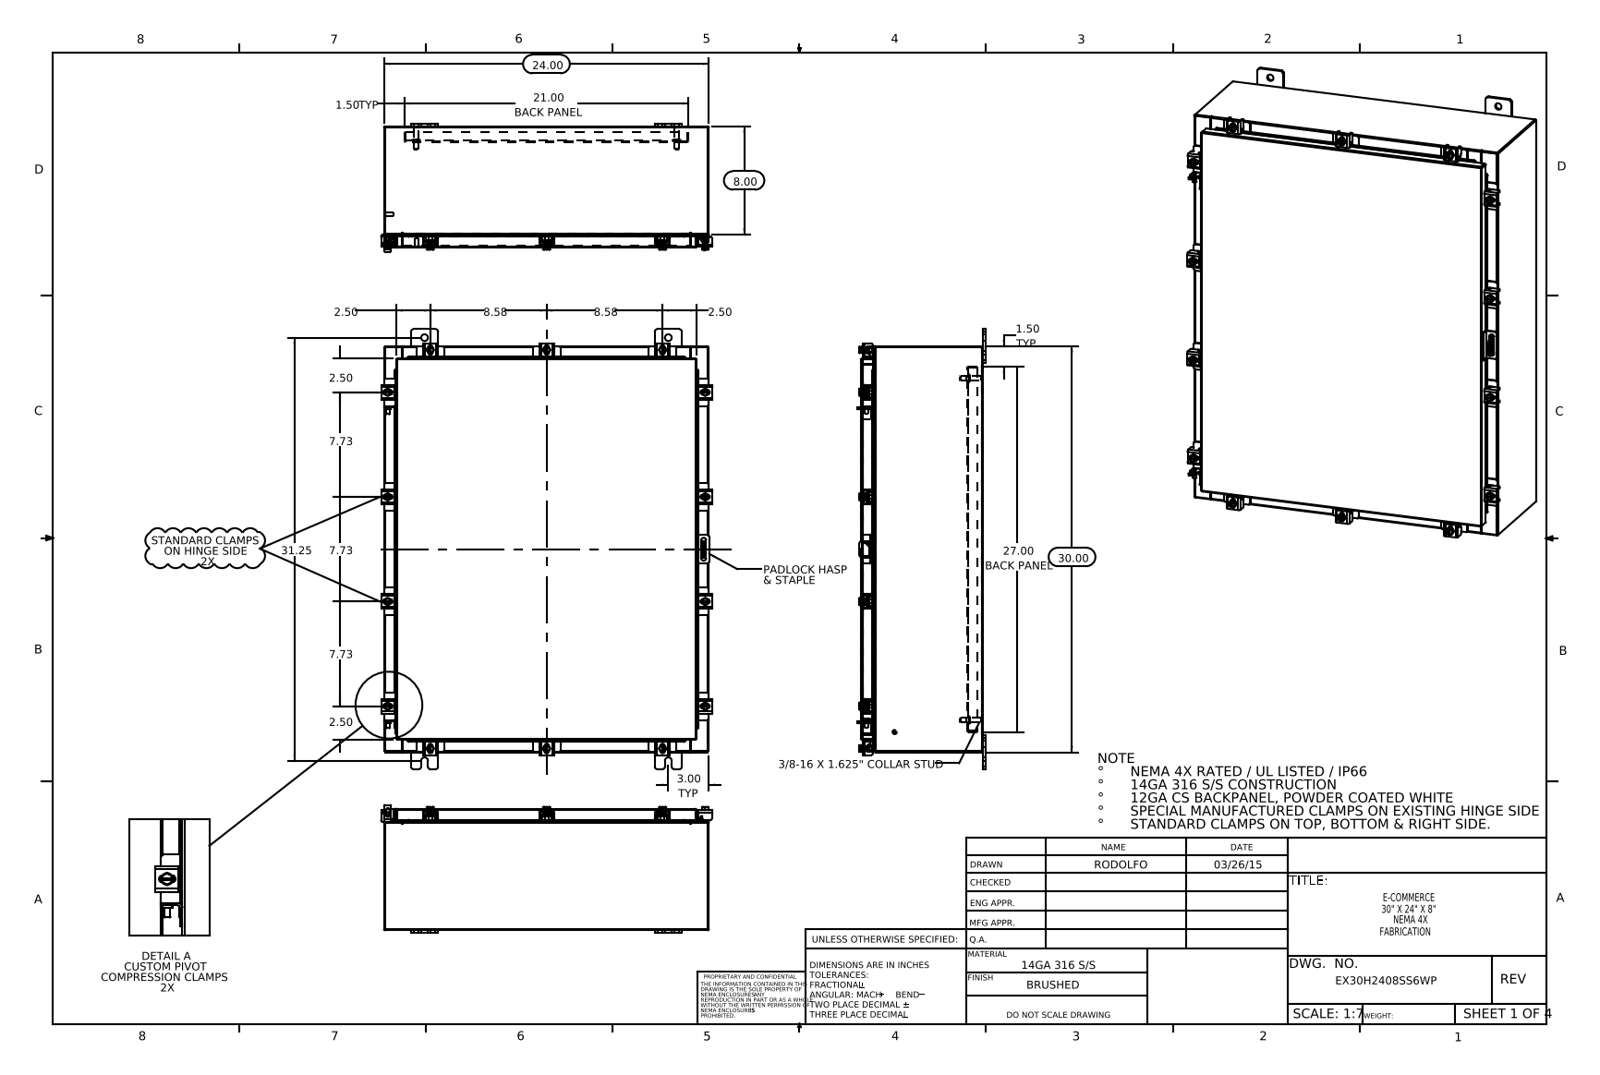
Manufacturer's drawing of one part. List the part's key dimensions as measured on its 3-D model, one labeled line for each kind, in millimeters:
Part name (STEP PRODUCT): EX30H2408SS6WP Backpanel; Quarter-20 CD Stud; N-WMT04X30402202210-00 22101002; EX30H2408SS6WP Bottom (+8 more)
STEP written by: SolidWorks 2014 (CONFIG_CONTROL_DESIGN)
Units: millimetres
Bodies: 91 solids, 2272 faces (1211 planar, 885 cylindrical, 176 other)
Overall size (bounding box): 825.5 × 620.3 × 240.1
Volume: 4 336 000 mm³ · Surface area: 4 241 000 mm²
Round holes (diameter × count): ⌀5.4 ×14, ⌀6.6 ×14, ⌀12.7 ×8, ⌀3.2 ×1, ⌀6.4 ×1
Round bosses / shafts (diameter × count): ⌀12.7 ×14, ⌀6.4 ×14, ⌀10.1 ×12, ⌀15.9 ×4, ⌀9.5 ×4, ⌀8.4 ×4, ⌀8 ×2, ⌀6 ×2
Partial cylindrical surfaces — rounded edges, fillets, slot ends (radius × count): R1.5 ×62, R3.6 ×28, R0.3 ×26, R3 ×26, R4.8 ×24, R2.2 ×22, R2.3 ×20, R1.3 ×19
Main face-to-face distances: 1.9, 226.1, 228, 224.2, 2.6, 25.4, 27.3, 198.8, 200.7, 29.9
Hole centre spacings: 59.6, 112.8, 521.8, 595.7, 617.5, 673.3, 695.2, 820.1
